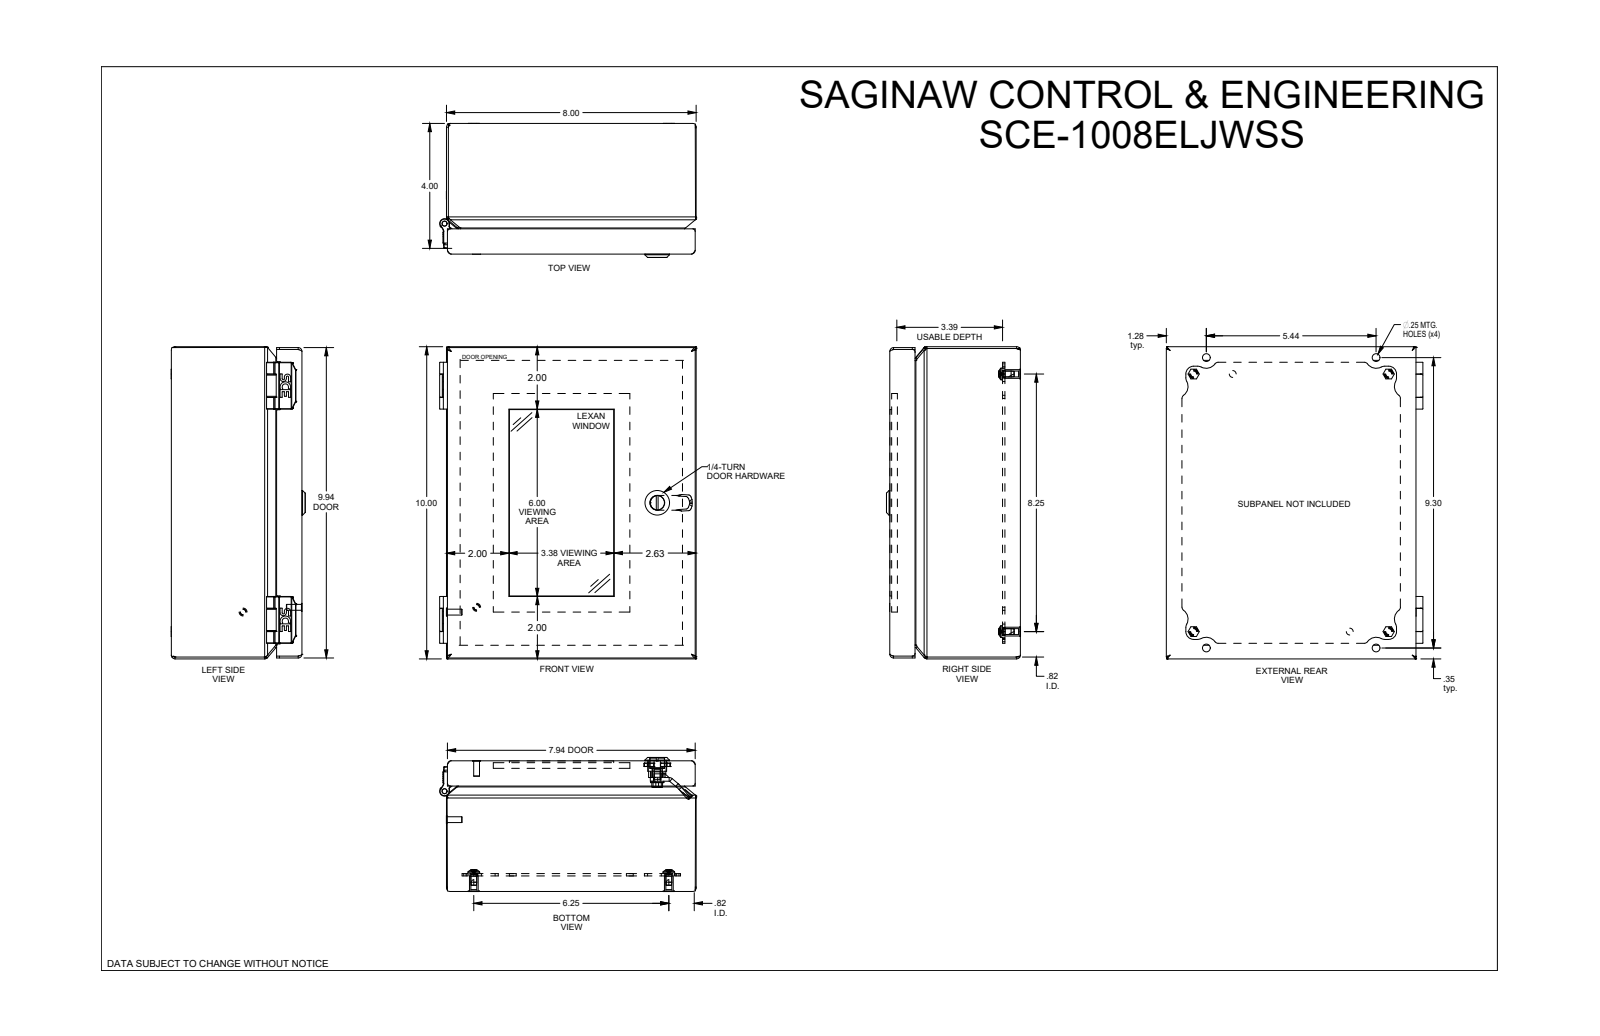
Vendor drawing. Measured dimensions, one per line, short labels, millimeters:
name: SCE-1008ELJW
written by: SolidWorks 2019 (AUTOMOTIVE_DESIGN)
unit: mm
bodies: 31 solids, 962 faces (377 planar, 317 cylindrical, 268 other)
size: 254 × 208.8 × 109.1
volume: 537 200 mm³; area: 565 700 mm²
holes: 4× ⌀4.8, 4× ⌀6.4, 4× ⌀7.2, 2× ⌀0.5, 2× ⌀2.5, 2× ⌀5.5, 2× ⌀6.8, 1× ⌀4, 1× ⌀5, 1× ⌀5.1, 1× ⌀6.1, 1× ⌀6.5
bosses: 6× ⌀4.8, 4× ⌀9.5, 4× ⌀7.1, 4× ⌀4.1, 2× ⌀6.6, 2× ⌀6.5, 2× ⌀6, 2× ⌀5.8
rounds: 28× R0.8, 21× R0.3, 16× R1.3, 13× R6.4, 11× R3.2, 10× R0.3, 10× R1.5, 8× R8.7
face distances: 1.5, 1.5, 104.9, 103.4, 12.7, 11.2, 13.1, 14.6, 90.3, 1.9
hole spacings: 31.8, 105.2, 127, 158.8, 182.4, 190.5, 209.6, 211.9
